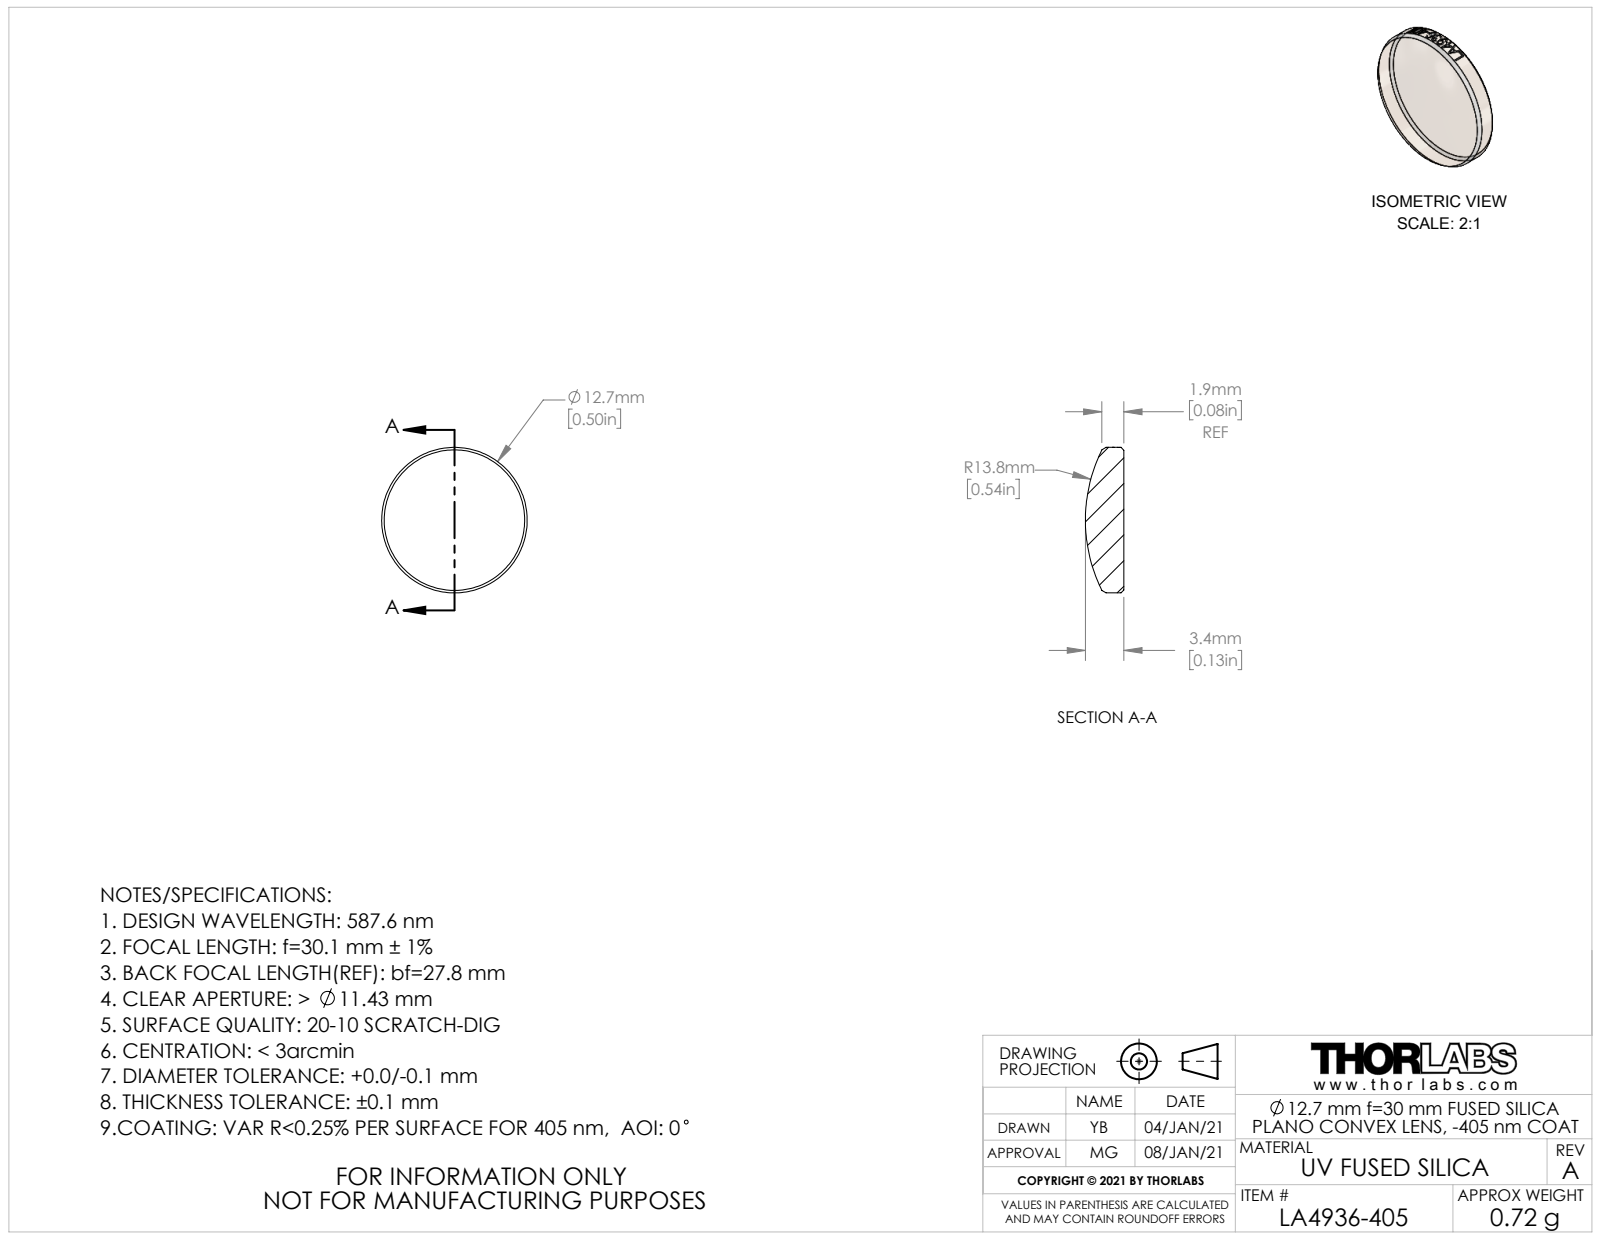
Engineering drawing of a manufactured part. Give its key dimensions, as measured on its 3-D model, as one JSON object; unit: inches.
{"part_name": "CTN016810-E0W; CTN016830", "step_written_by": "SolidWorks 2018 (AUTOMOTIVE_DESIGN)", "units": "inches", "bodies": {"solids": 1, "faces": 31, "planar": 1, "cylindrical": 24, "other": 6}, "overall_size": [0.5, 0.5, 0.132], "volume_in3": 0.02, "surface_area_in2": 0.502, "round_bosses_or_shafts": [[0.5, 1]]}
